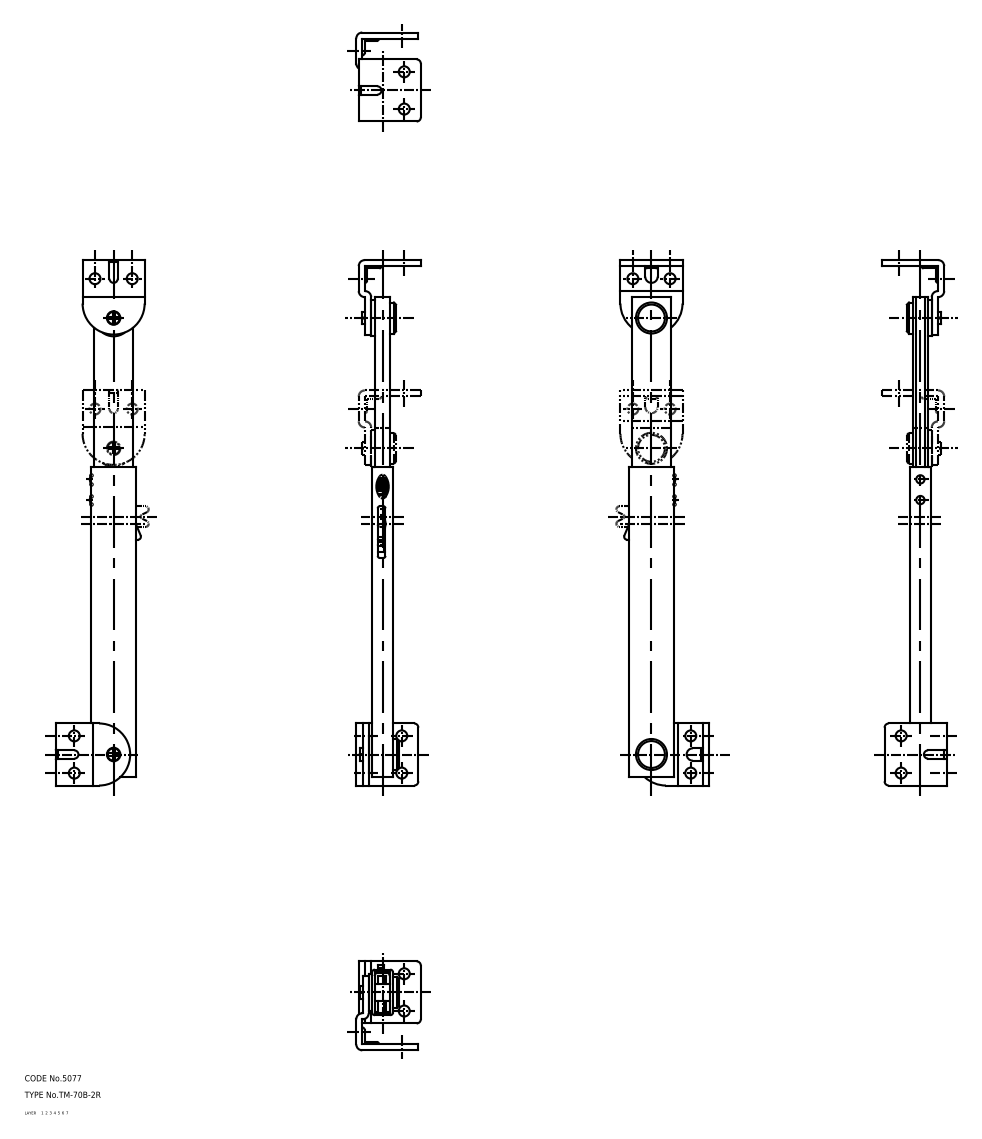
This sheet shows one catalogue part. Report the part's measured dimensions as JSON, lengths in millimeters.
{"part_name": "bracket_A; rivet_3; rivet_2; rivet_1 (+7 more)", "step_written_by": "CADfix (AUTOMOTIVE_DESIGN)", "units": "millimeters", "bodies": {"solids": 12, "faces": 299, "planar": 0, "cylindrical": 0, "other": 299}, "overall_size": [254, 43, 31.2], "volume_mm3": 33962, "surface_area_mm2": 42522}
